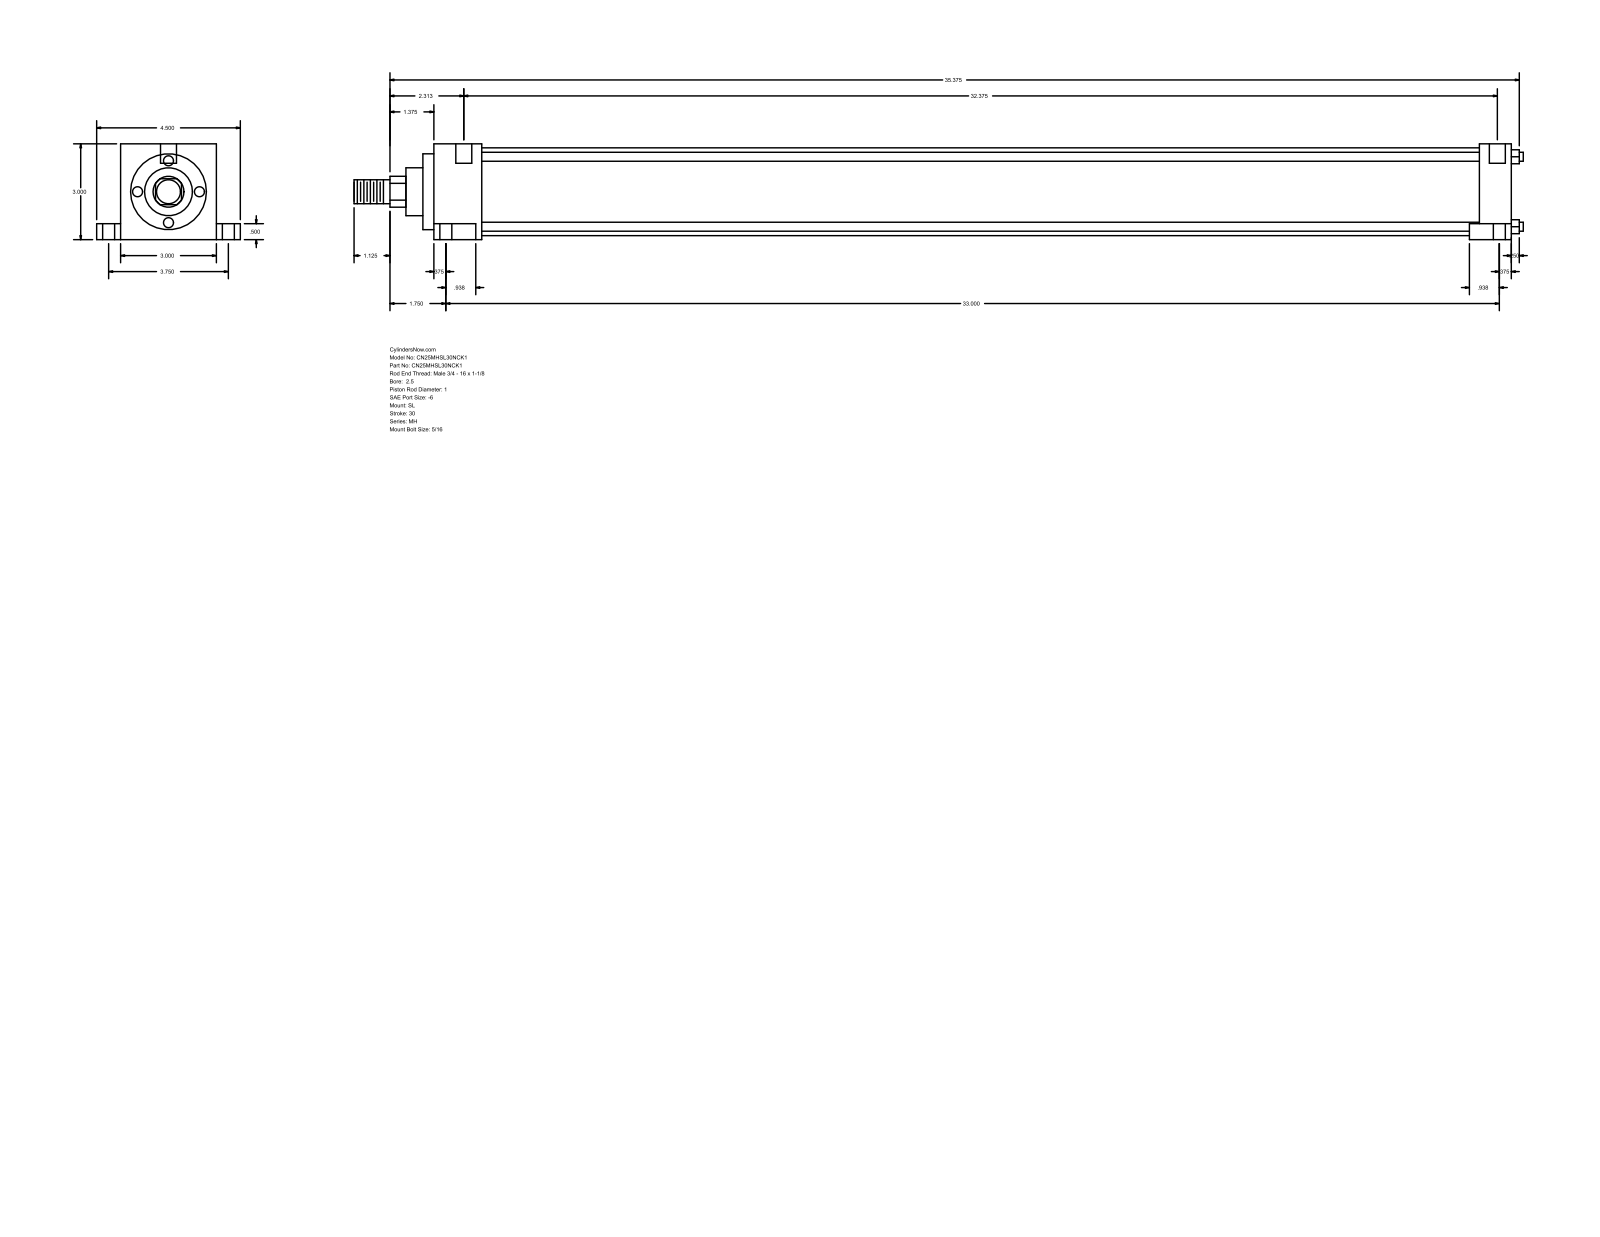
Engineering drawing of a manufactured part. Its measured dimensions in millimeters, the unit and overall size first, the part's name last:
Units: millimetres
Overall size (bounding box): 930.27 × 114.3 × 76.2
Round holes (diameter × count): ⌀5.56 ×2, ⌀9.53 ×2, ⌀15.88 ×2, ⌀12.7 ×1
Round bosses / shafts (diameter × count): ⌀7.14 ×4, ⌀69.85 ×1, ⌀60.33 ×1, ⌀38.1 ×1, ⌀25.4 ×1, ⌀19.05 ×1
Partial cylindrical surfaces — rounded edges, fillets, slot ends (radius × count): R12.29 ×1
Main face-to-face distances: 76.2, 25.4, 840.58, 865.98, 12.7, 63.5, 19.05, 95.25, 13.49, 854.07
Hole centre spacings: 47.65, 3.18, 95.24
Bodies: 0 solids, 86 faces (61 planar, 25 cylindrical, 0 other)
Part name (STEP PRODUCT): MH_SL__0250_1
STEP written by: GSSL Pune (CONFIG_CONTROL_DESIGN)
